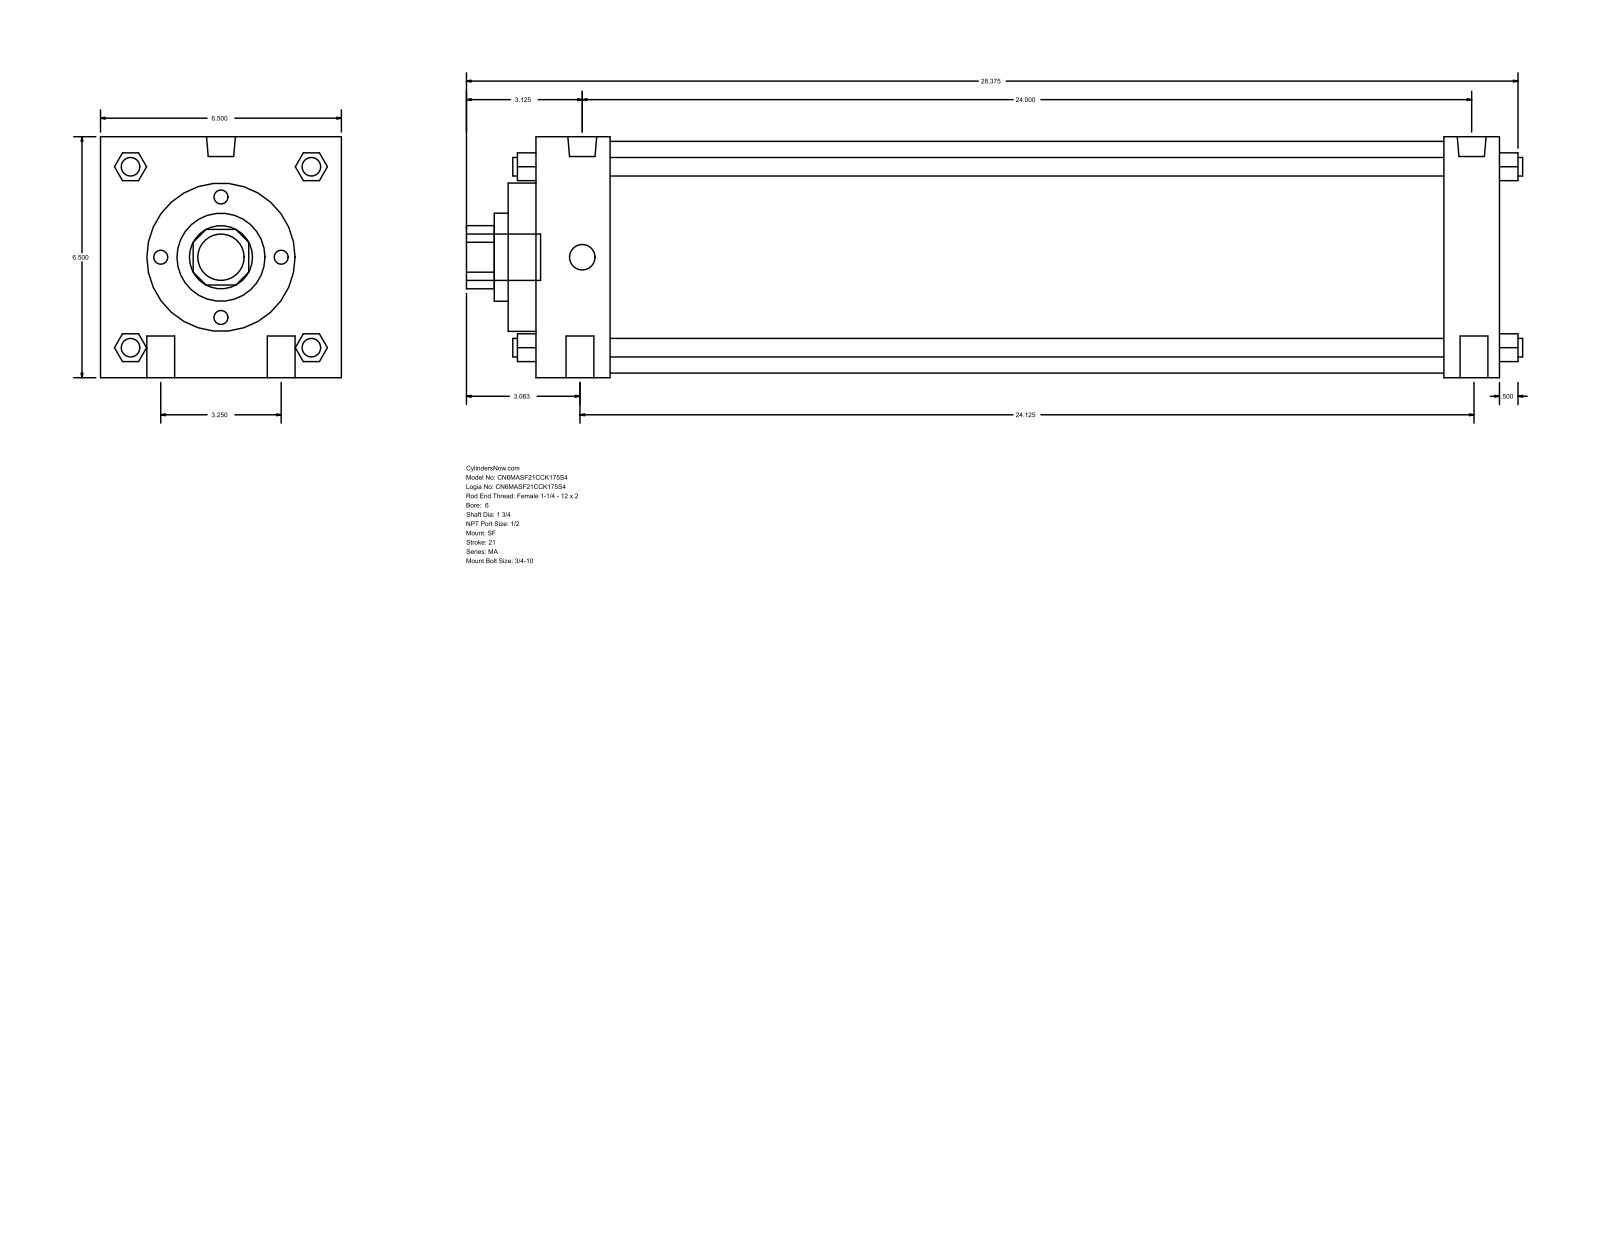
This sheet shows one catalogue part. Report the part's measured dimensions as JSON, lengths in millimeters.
{"part_name": "MA_SF__0600_1.75", "step_written_by": "GSSL Pune (CONFIG_CONTROL_DESIGN)", "units": "millimeters", "bodies": {"solids": 0, "faces": 126, "planar": 95, "cylindrical": 31, "other": 0}, "overall_size": [723.9, 165.1, 165.1], "round_holes": [[44.45, 1], [60.33, 1], [101.6, 1], [158.75, 1]], "round_bosses_or_shafts": [[19.05, 4], [12.7, 4], [19.77, 2], [17.46, 2], [31.75, 1]], "partial_cylinders_radius": [[21.63, 1]], "face_to_face_distances": [165.1, 660.4, 19.05, 50.8, 38.1, 622.3, 571.5, 609.6, 69.85, 641.35]}
